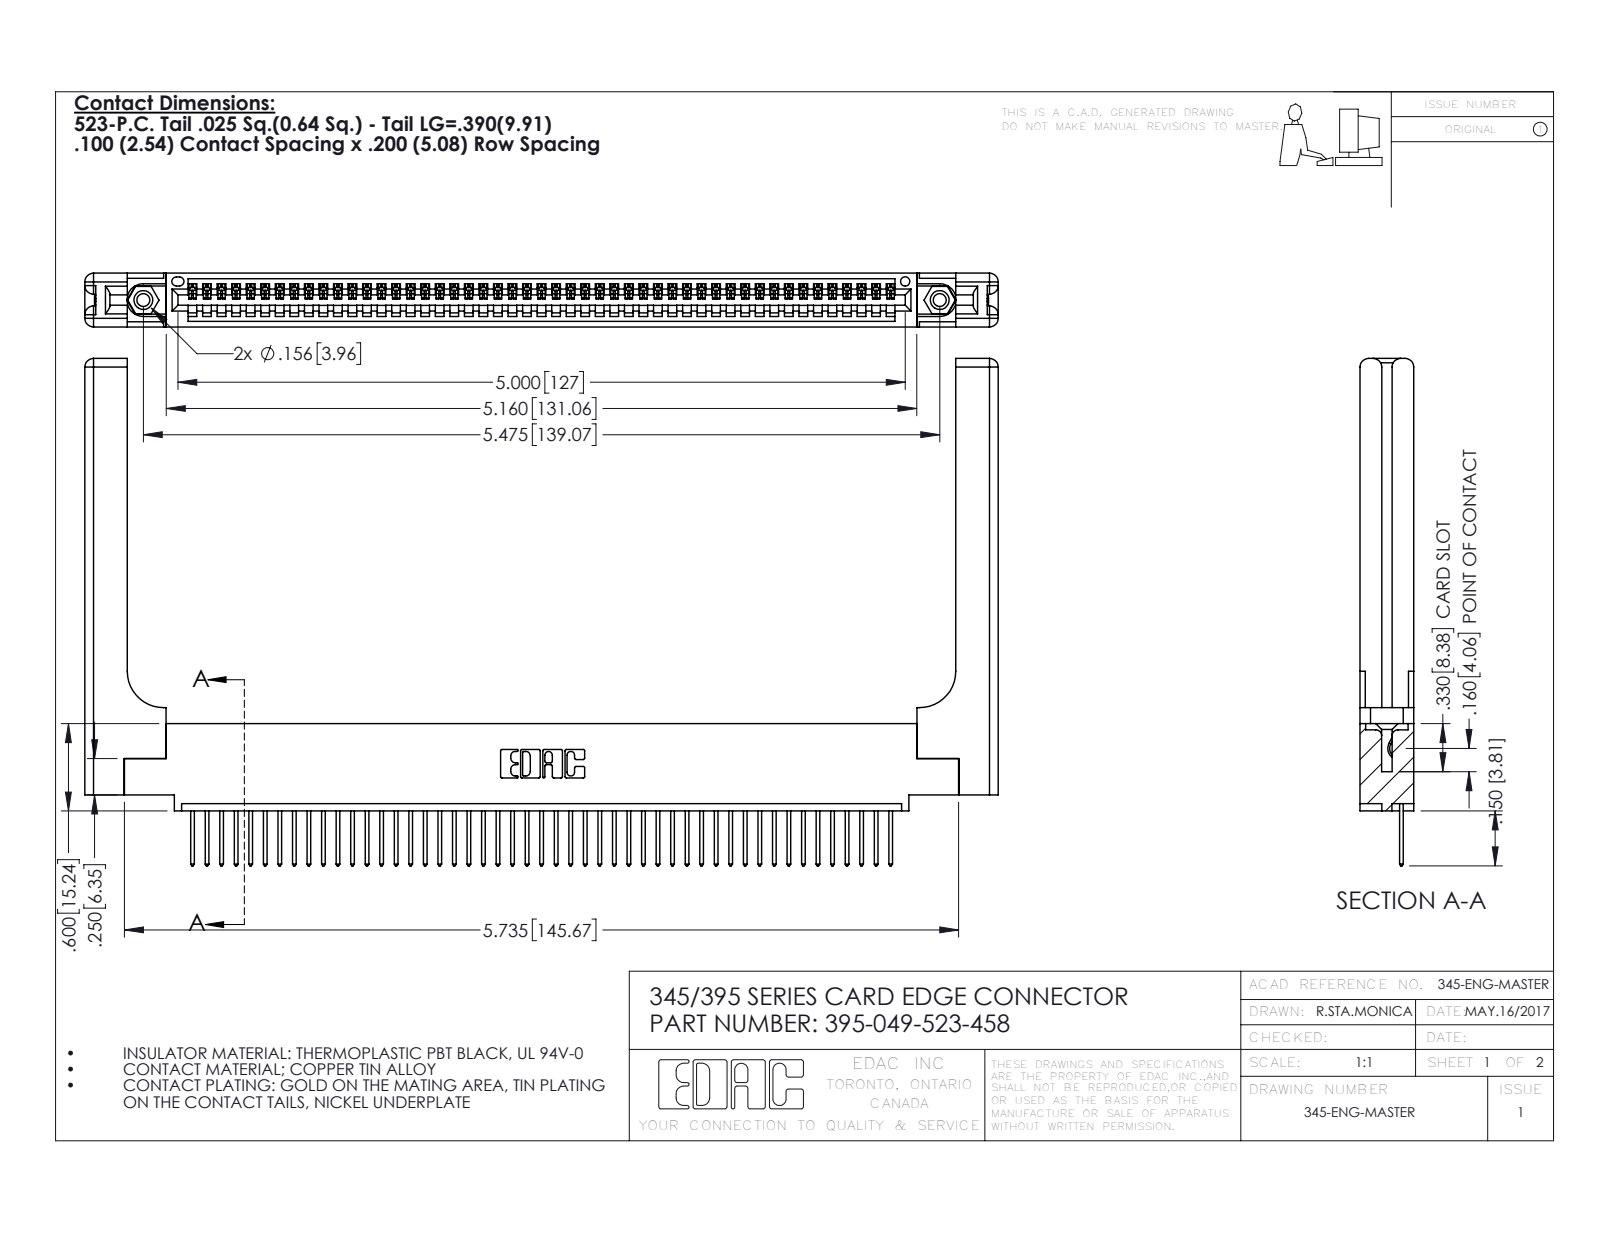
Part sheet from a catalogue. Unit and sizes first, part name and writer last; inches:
Units: inches
Overall size (bounding box): 6.279 × 3.487 × 0.37
Round holes (diameter × count): ⌀0.089 ×2, ⌀0.125 ×2, ⌀0.156 ×2, ⌀0.064 ×1
Round bosses / shafts (diameter × count): ⌀0.155 ×2
Partial cylindrical surfaces — rounded edges, fillets, slot ends (radius × count): R0.006 ×98, R0.01 ×98, R0.01 ×22, R0.06 ×16, R0.007 ×6, R0.031 ×6, R0.026 ×3, R0.03 ×2
Main face-to-face distances: 0.072, 0.37, 0.298, 0.098, 0.272, 0.025, 0.2, 0.225, 0.148, 0.15
Hole centre spacings: 0.27, 5.239, 5.475
Volume: 1.441 in³ · Surface area: 39.71 in²
Bodies: 54 solids, 3228 faces (2192 planar, 976 cylindrical, 60 other)
Part name (STEP PRODUCT): 345-220-058_345-220-058; 345-292-001_345-293-123; 345-250-001_345-250-001-102; 395-049-523-458 (+1 more)
STEP written by: SolidWorks 2016 (CONFIG_CONTROL_DESIGN)
